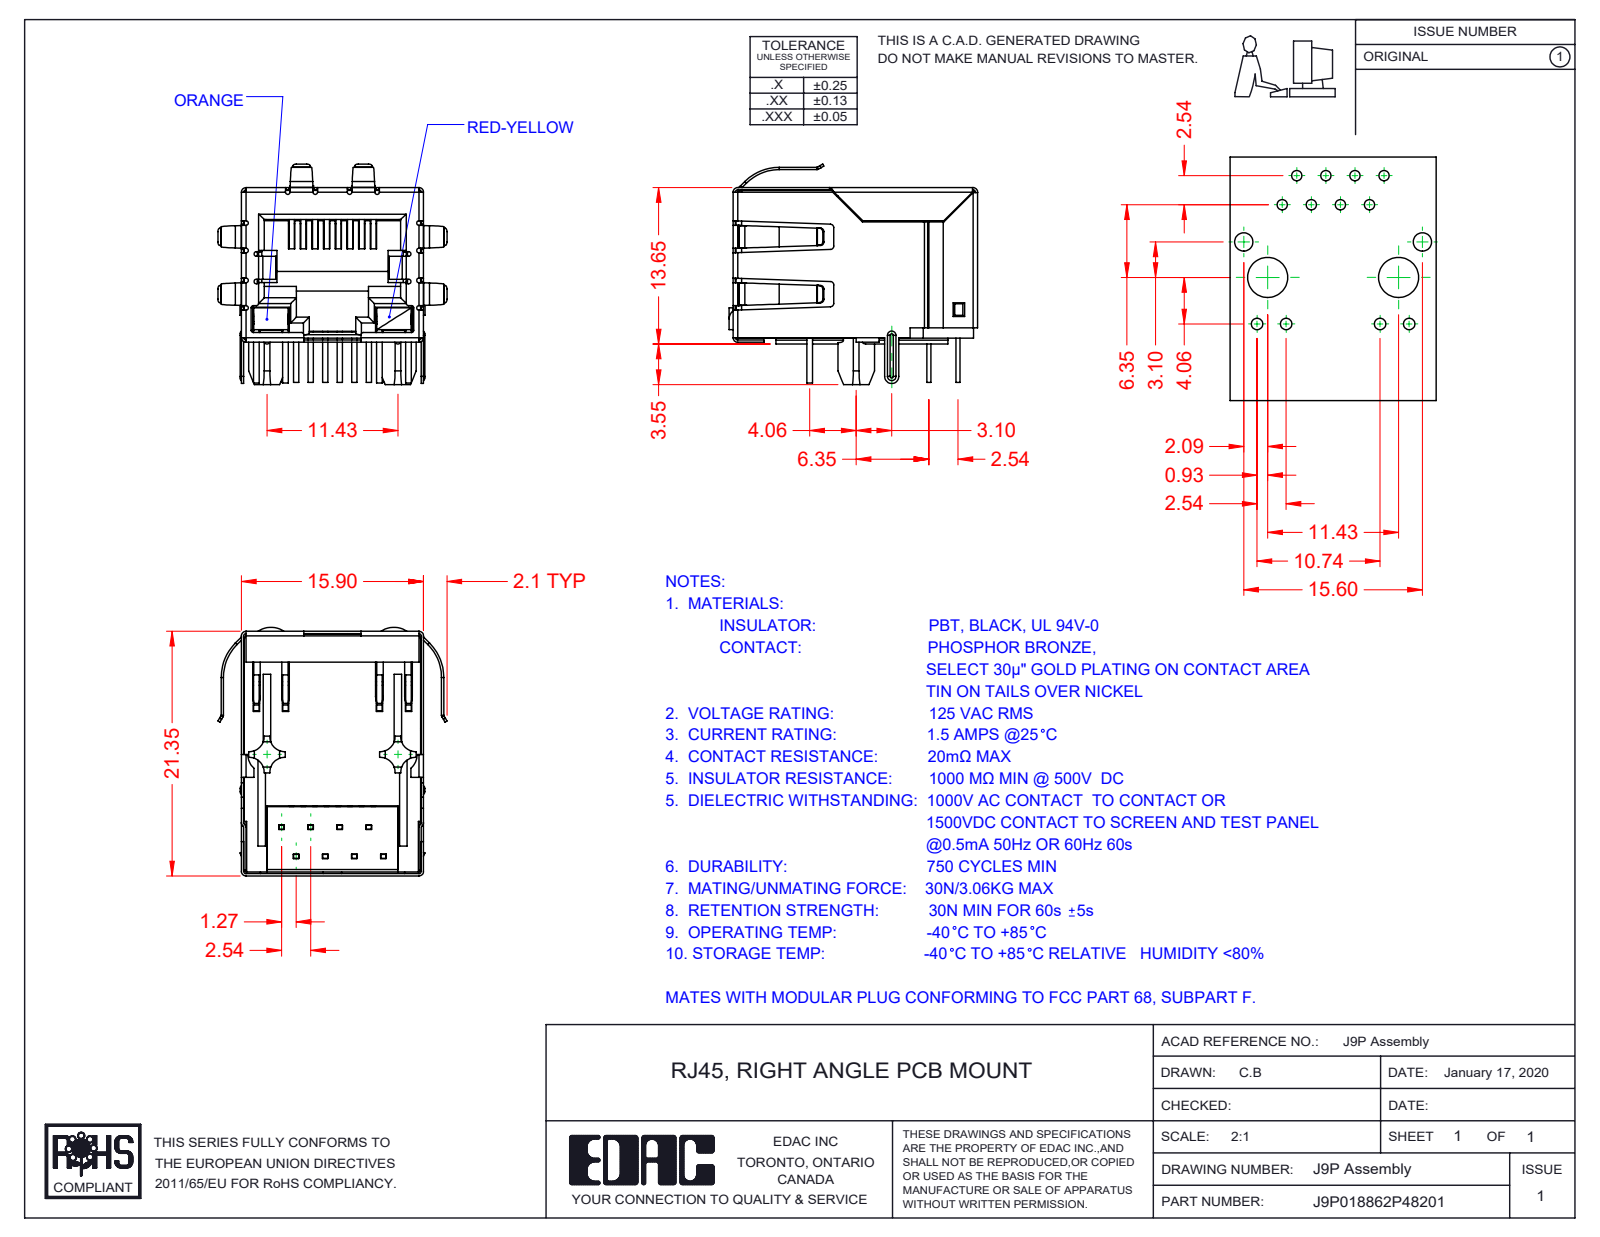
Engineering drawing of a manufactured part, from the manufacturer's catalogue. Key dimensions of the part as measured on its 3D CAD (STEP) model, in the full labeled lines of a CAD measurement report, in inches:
Part name (STEP PRODUCT): 9P-LED Shield; 9P-LED LED RH_8-Red-Yellow; 9P-LED Assembly; 9P-LED Contacts (+4 more)
STEP written by: SolidWorks 2016 (CONFIG_CONTROL_DESIGN)
Units: inches
Bodies: 13 solids, 1474 faces (1042 planar, 338 cylindrical, 94 other)
Overall size (bounding box): 0.854 × 0.787 × 0.758
Volume: 0.164 in³ · Surface area: 11.65 in²
Partial cylindrical surfaces — rounded edges, fillets, slot ends (radius × count): R0.008 ×39, R0.02 ×22, R0.012 ×20, R0.016 ×16, R0.051 ×8, R0.009 ×5, R0.004 ×4, R0.012 ×4
Main face-to-face distances: 0.608, 0.618, 0.616, 0.014, 0.021, 0.61, 0.487, 0.024, 0.055, 0.023
